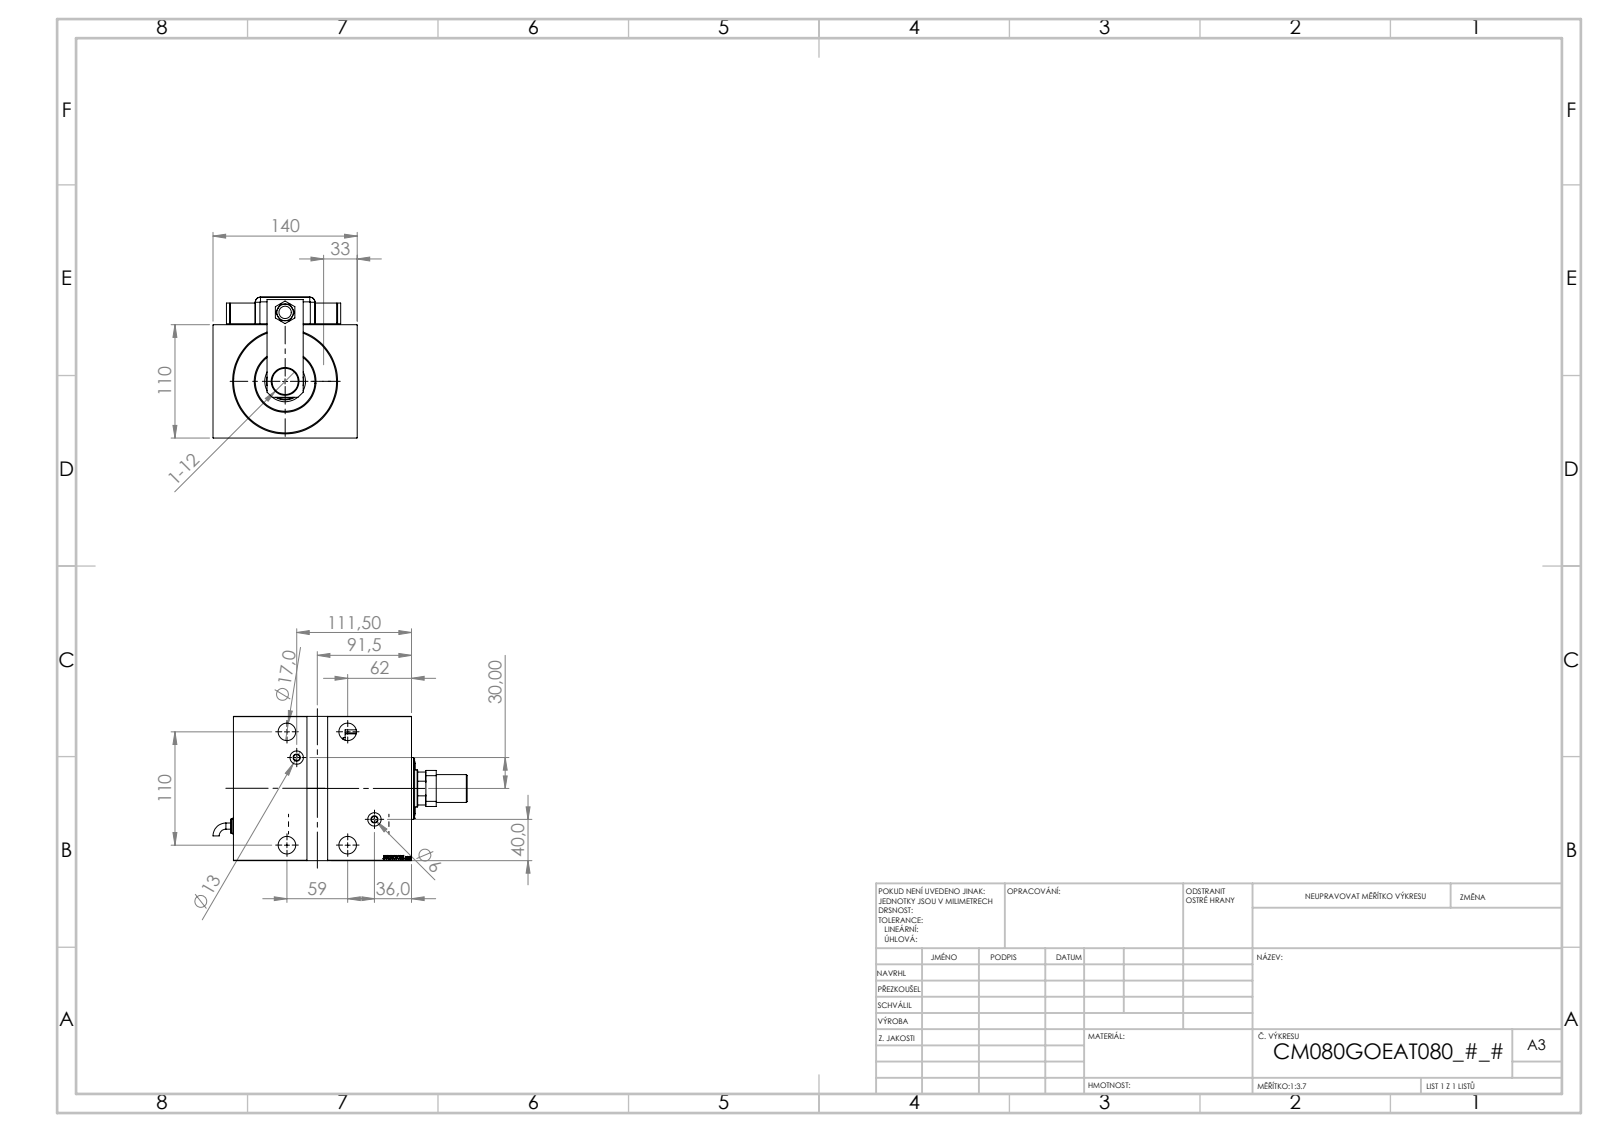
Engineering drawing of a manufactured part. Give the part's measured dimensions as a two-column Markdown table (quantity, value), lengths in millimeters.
| quantity | value |
| --- | --- |
| part name | ZARAZKA_Q; SWITCH DIM A_G; V450CM_VC_G; SWITCH Q (+7 more) |
| STEP written by | SolidWorks 2019 (CONFIG_CONTROL_DESIGN) |
| units | millimeters |
| bodies | 16 solids, 1294 faces (652 planar, 115 cylindrical, 527 other) |
| overall size | 246.76 × 140 × 136.8 |
| volume | 2 379 000 mm³ |
| surface area | 320 819 mm² |
| round holes (diameter × count) | 17 × 4, 25 × 4, 13 × 3, 4 × 2, 6 × 2, 8 × 2, 12 × 1, 14 × 1, 25.5 × 1, 27 × 1, 36 × 1, 39.5 × 1 |
| round bosses / shafts (diameter × count) | 20 × 3, 26 × 2, 16 × 2, 14 × 2, 7 × 2, 6 × 2, 60 × 1, 25 × 1 |
| partial cylindrical surfaces (radius × count) | 5 × 9, 10 × 1, 17.5 × 1 |
| main face-to-face distances | 110, 140, 3, 21, 173, 5, 152, 168, 147, 136.8 |
| hole center spacings | 59, 71.06, 85.15, 110, 122.56, 124.82, 131.23, 20 |
